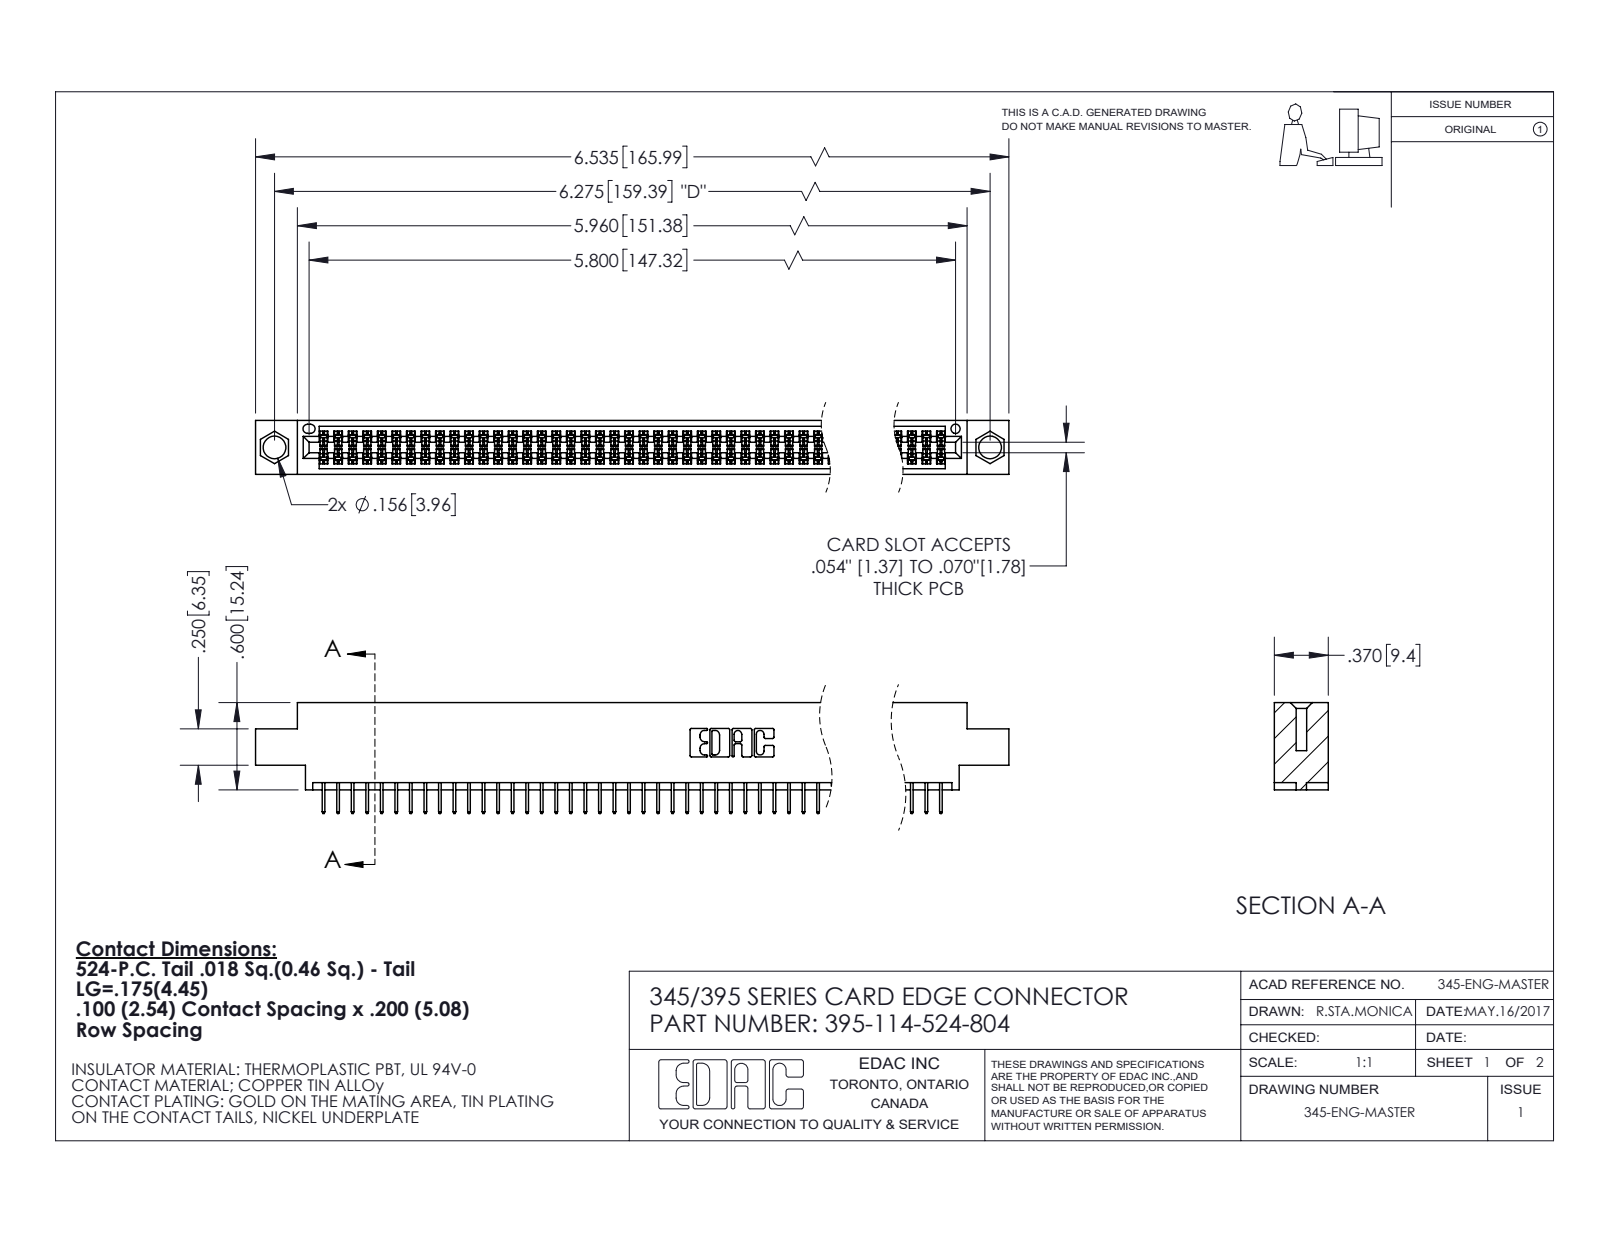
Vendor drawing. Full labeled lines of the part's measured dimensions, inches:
Part name (STEP PRODUCT): 345-292-001_345-293-124; 395-114-524-804; 345 Part_0.170 Offset - 0.156 Dia-TI
STEP written by: SolidWorks 2020 (CONFIG_CONTROL_DESIGN)
Units: inches
Bodies: 115 solids, 6300 faces (4544 planar, 1756 cylindrical, 0 other)
Overall size (bounding box): 6.535 × 0.762 × 0.37
Volume: 0.969 in³ · Surface area: 36.1 in²
Round holes (diameter × count): ⌀0.156 ×2, ⌀0.064 ×1
Partial cylindrical surfaces — rounded edges, fillets, slot ends (radius × count): R0.006 ×228, R0.01 ×22, R0.007 ×6, R0.031 ×6, R0.026 ×3, R0.014 ×2, R0.019 ×2, R0.022 ×2
Main face-to-face distances: 0.072, 0.298, 0.37, 0.2, 0.098, 0.272, 0.025, 0.225, 0.072, 0.175
Hole centre spacings: 0.27, 6.039, 6.275
